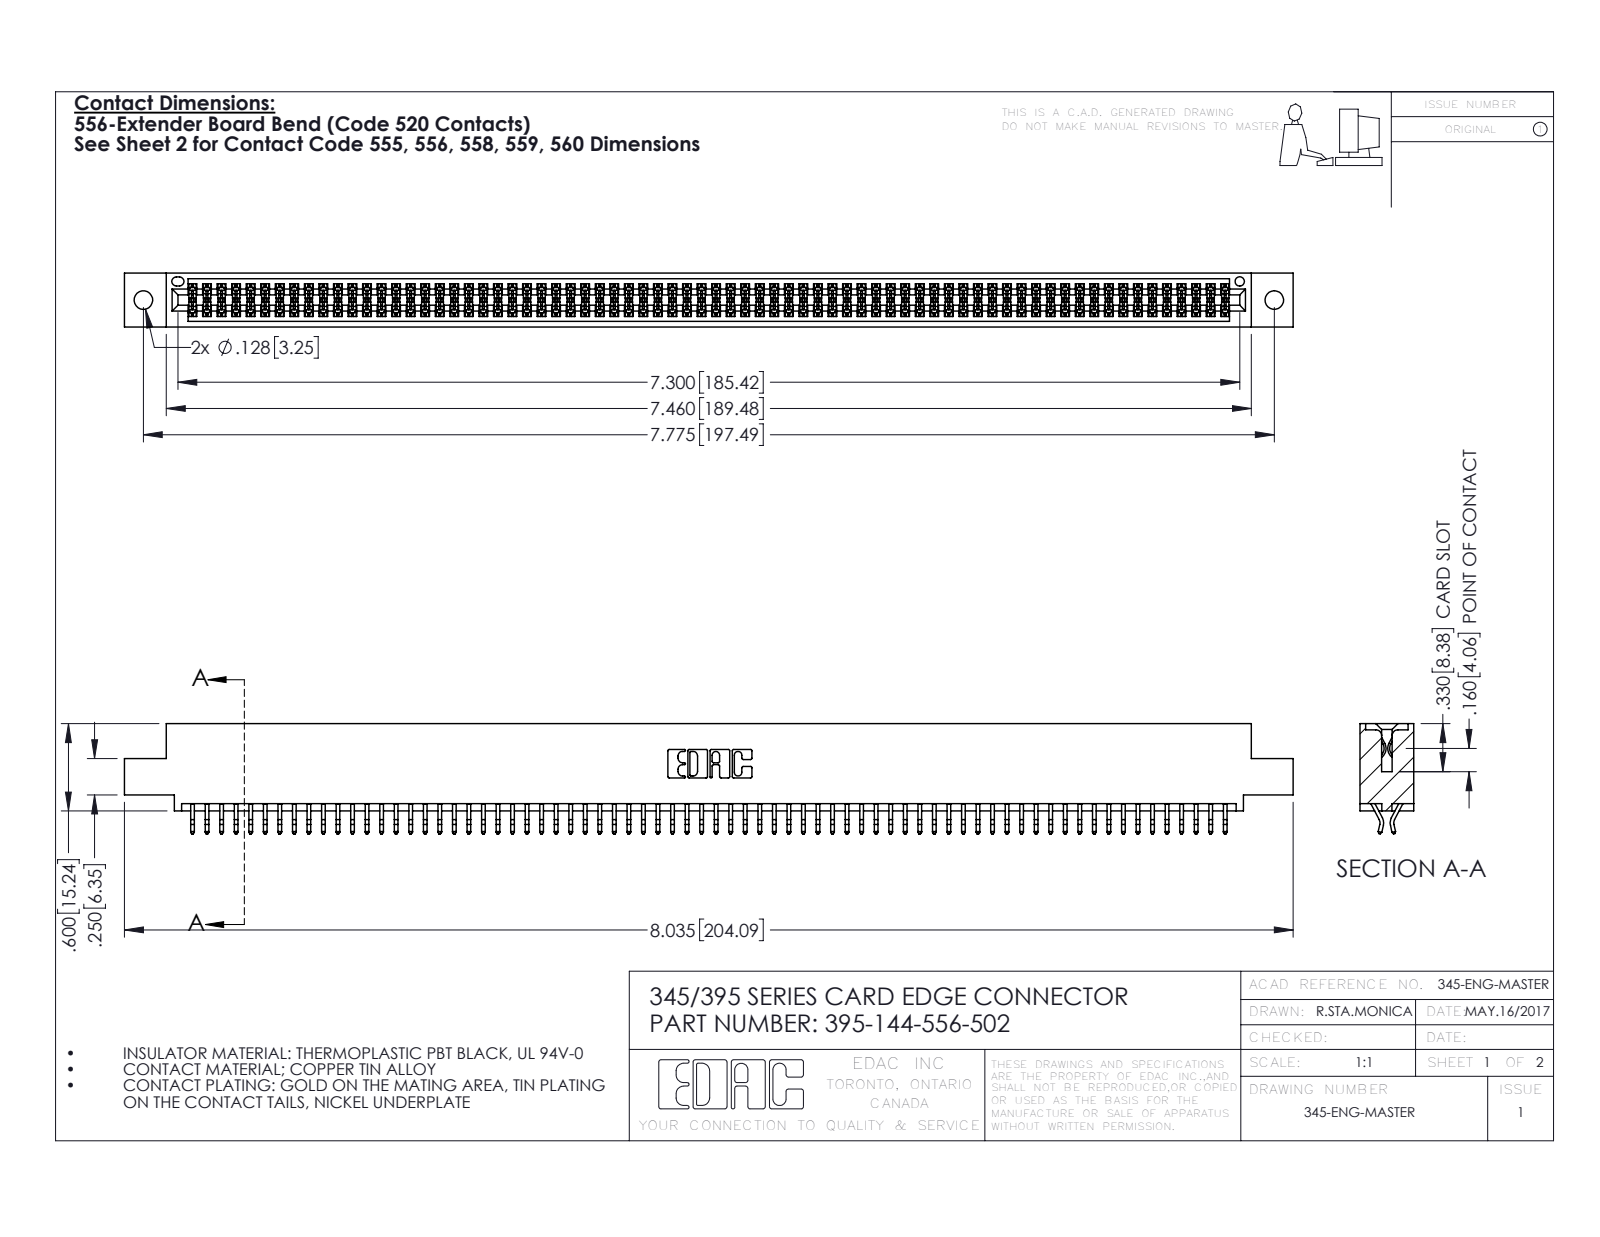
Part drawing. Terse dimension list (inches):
name: 395-144-556-502; 345 Part_0.110 Offset - 0.128 Dia; 345-292-001_556 Tail
written by: SolidWorks 2016 (CONFIG_CONTROL_DESIGN)
unit: in
bodies: 145 solids, 8194 faces (5412 planar, 2782 cylindrical, 0 other)
size: 8.035 × 0.757 × 0.37
volume: 1.22 in³; area: 46.22 in²
holes: 2× ⌀0.128, 1× ⌀0.064
rounds: 216× R0.006, 22× R0.01, 6× R0.007, 6× R0.031, 3× R0.026, 2× R0.01, 2× R0.014, 2× R0.019
face distances: 0.298, 0.072, 0.37, 0.2, 0.025, 0.098, 0.272, 0.225, 0.175, 0.149
hole spacings: 0.27, 7.539, 7.775
